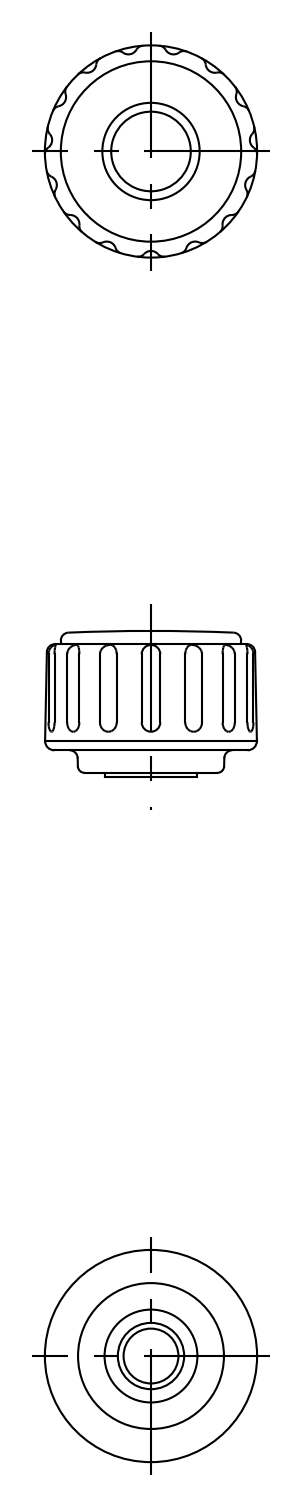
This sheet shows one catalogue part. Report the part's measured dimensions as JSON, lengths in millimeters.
{"part_name": "screw; knob; KDFS_16_M5_WH_1854_36", "step_written_by": "CADfix (AUTOMOTIVE_DESIGN)", "units": "millimeters", "bodies": {"solids": 2, "faces": 65, "planar": 0, "cylindrical": 0, "other": 65}, "overall_size": [16.12, 15.97, 10.96], "volume_mm3": 1722, "surface_area_mm2": 1193}
